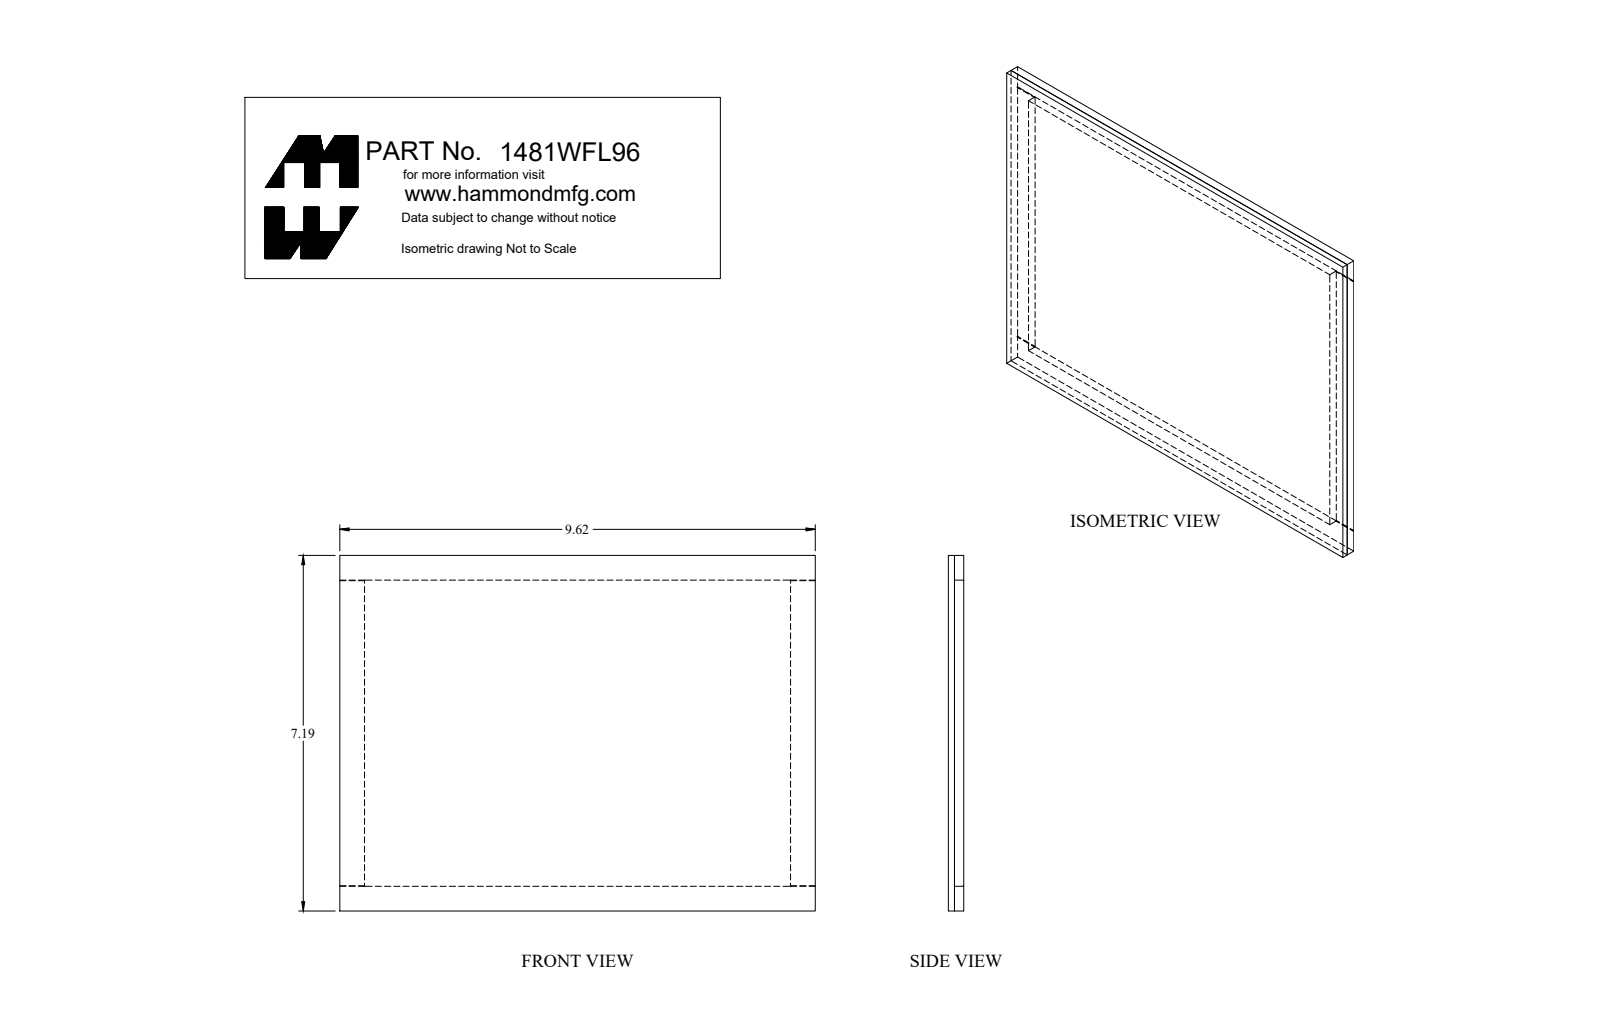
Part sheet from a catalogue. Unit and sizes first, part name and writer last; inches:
Units: inches
Overall size (bounding box): 9.62 × 7.19 × 0.313
Main face-to-face distances: 0.125, 0.313, 0.187, 0.5, 6.69, 7.19, 9.12, 9.62, 6.19, 8.62
Volume: 11.61 in³ · Surface area: 186.1 in²
Bodies: 2 solids, 27 faces (27 planar, 0 cylindrical, 0 other)
Part name (STEP PRODUCT): 1481WFL96_Default
STEP written by: SolidWorks 2019 (CONFIG_CONTROL_DESIGN)
